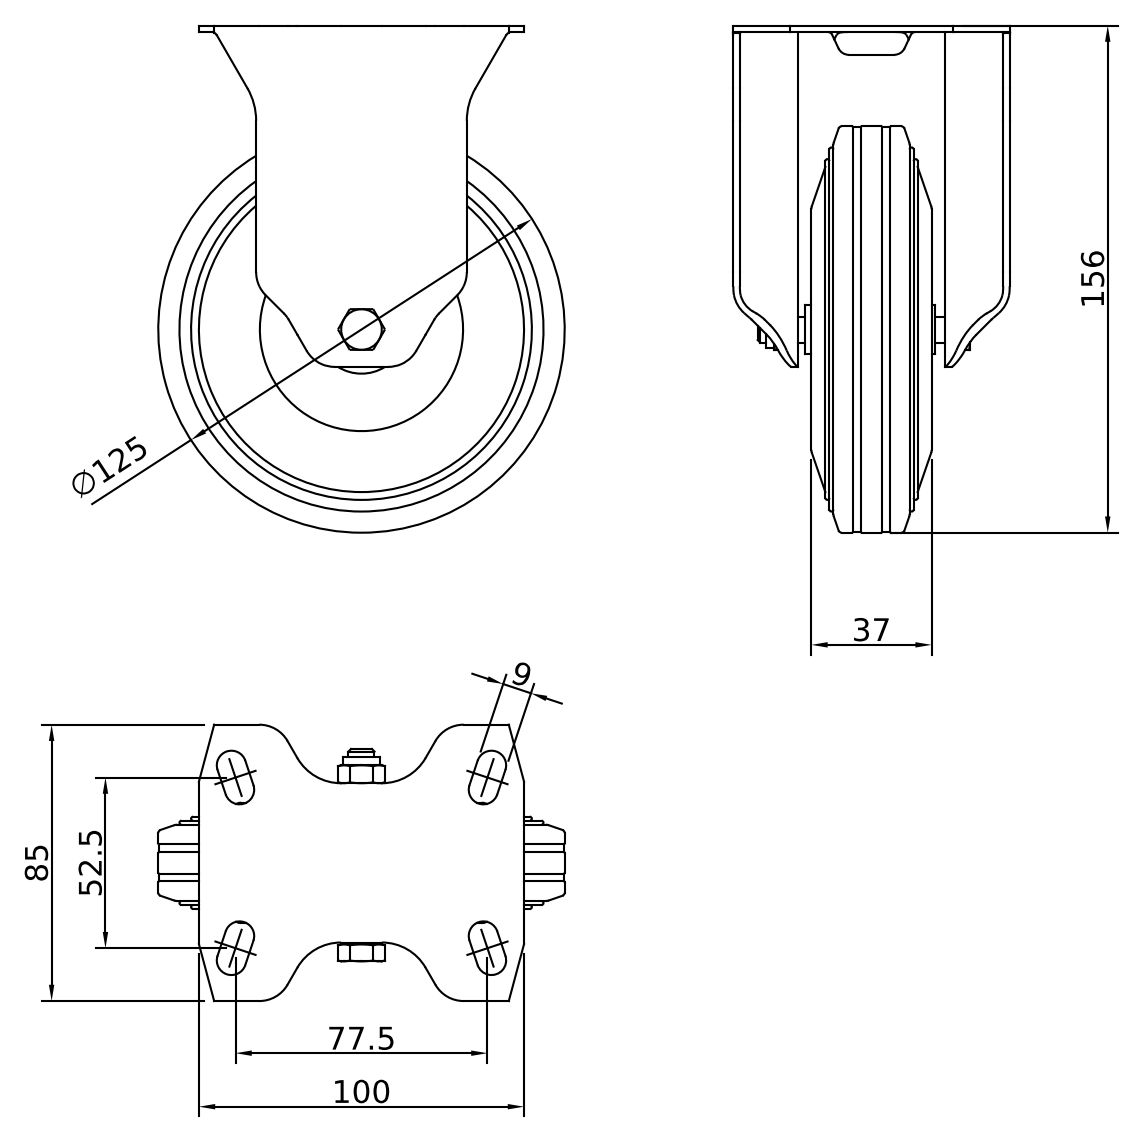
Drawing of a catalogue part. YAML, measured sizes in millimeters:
part_name: "CRUST0000039; 440000025851; 440000025850; 440000025849"
step_written_by: "Autodesk Inventor 2022 (AUTOMOTIVE_DESIGN)"
units: millimeters
bodies: {solids: 3, faces: 242, planar: 101, cylindrical: 78, other: 63}
overall_size: [156, 125, 85]
volume: 385584
surface_area: 91071
round_holes:
  - {diameter: 9, count: 1}
  - {diameter: 15, count: 1}
round_bosses_or_shafts:
  - {diameter: 125, count: 1}
  - {diameter: 124.4, count: 1}
  - {diameter: 11.63, count: 1}
  - {diameter: 8, count: 1}
partial_cylinders:
  - {radius: 10, count: 10}
  - {radius: 1.5, count: 8}
  - {radius: 3.5, count: 8}
  - {radius: 4.5, count: 8}
  - {radius: 7, count: 4}
  - {radius: 8, count: 4}
  - {radius: 15.5, count: 4}
  - {radius: 17.5, count: 4}
face_to_face_distances: [2, 43, 6, 4, 47, 41, 11.54, 37.46, 9.54, 35.46]
